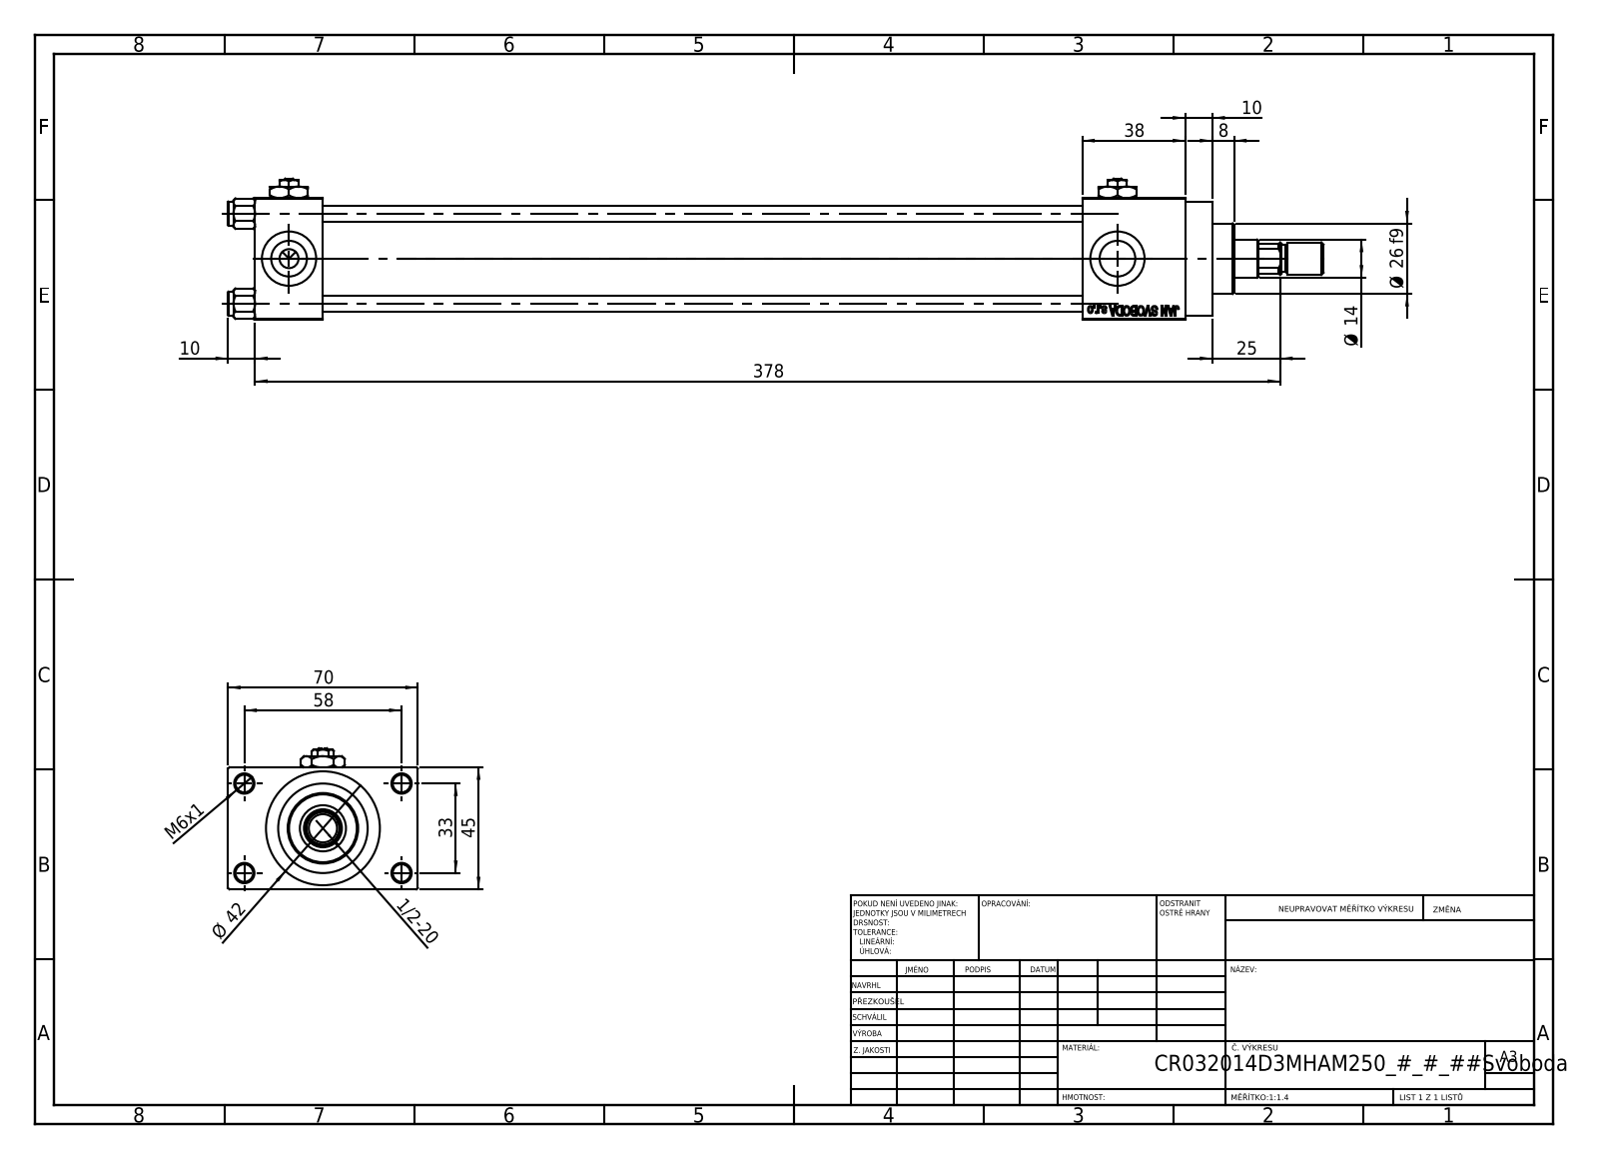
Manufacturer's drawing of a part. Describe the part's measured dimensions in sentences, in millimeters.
The part is named "NUT_M5_D; V215CR_D_Body; V215CR_D_TYCINKA; V215_VC_A (+3 more)". Its 3-D file was written by "SolidWorks 2019 (CONFIG_CONTROL_DESIGN)". It is 14 solids with 1215 faces: 546 planar, 103 cylindrical and 566 other. Overall it measures 404 by 70 by 52 millimeters. Its volume is 368 089 cubic millimeters and its surface area 156 015 square millimeters. Round holes: 5 of diameter 6.5, 4 of diameter 6, 4 of diameter 13.16, 4 of diameter 20, 3 of diameter 7, 1 of diameter 14, 1 of diameter 17, 1 of diameter 24, 1 of diameter 32, 1 of diameter 33. Round bosses or shafts: 4 of diameter 9, 1 of diameter 42, 1 of diameter 38, 1 of diameter 26, 1 of diameter 12, 1 of diameter 10. Partial cylindrical surfaces (rounded edges, fillets, slot ends): 1 of radius 6.5. The main face-to-face distances are 45, 25, 12.5, 280, 305, 57.5, 318, 38, 343, 70. The hole center spacings are 12.4, 23.48, 33.2, 33.37, 35.35, 45.6, 56.35, 33.
